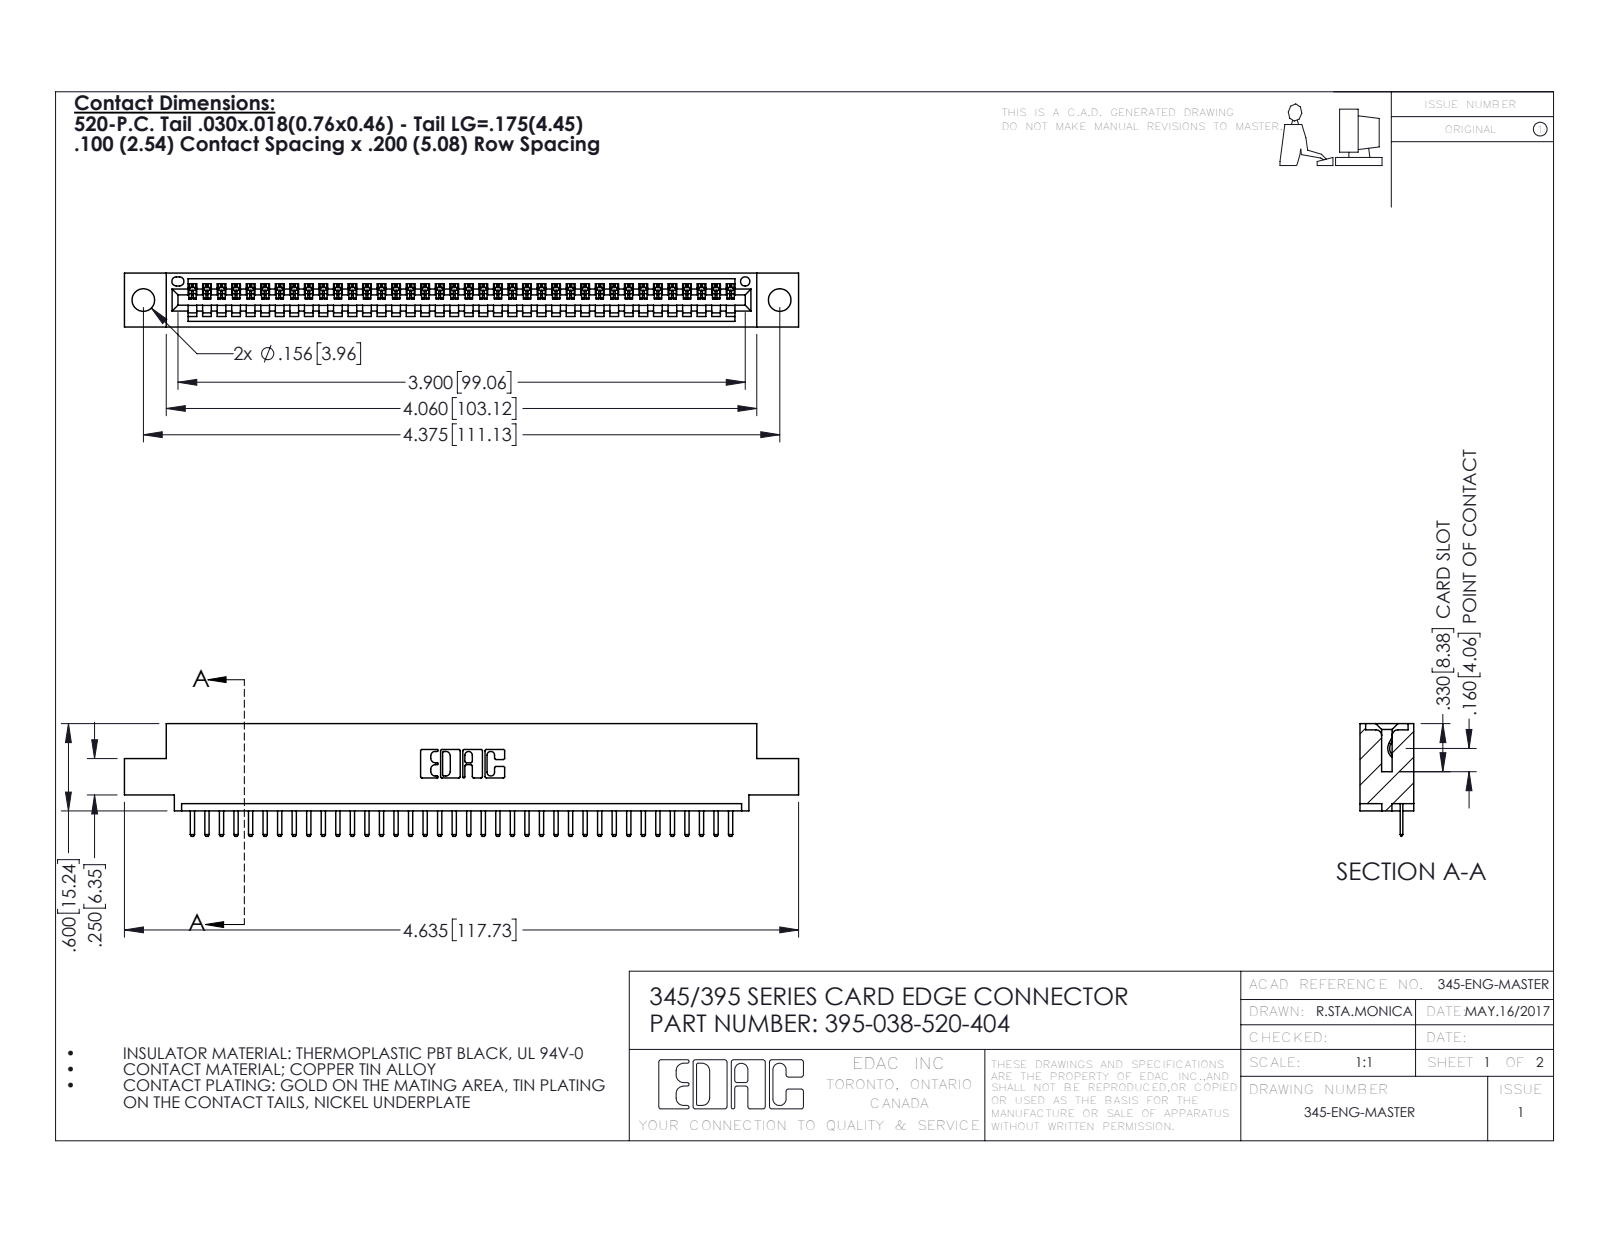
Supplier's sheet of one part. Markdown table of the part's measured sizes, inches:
| quantity | value |
| --- | --- |
| part name | 345 Part_0.110 Offset - 0.156 Dia-TH; 395-038-520-404; 345-292-001_345-293-120 |
| STEP written by | SolidWorks 2016 (CONFIG_CONTROL_DESIGN) |
| units | inches |
| bodies | 39 solids, 2486 faces (1680 planar, 806 cylindrical, 0 other) |
| overall size | 4.635 × 0.775 × 0.37 |
| volume | 0.664 in³ |
| surface area | 21.6 in² |
| round holes (diameter × count) | 0.156 × 2, 0.064 × 1 |
| partial cylindrical surfaces (radius × count) | 0.01 × 78, 0.006 × 76, 0.01 × 22, 0.007 × 6, 0.031 × 6, 0.026 × 3, 0.031 × 2, 0.04 × 2 |
| main face-to-face distances | 0.298, 0.072, 0.37, 0.2, 0.098, 0.272, 0.025, 0.225, 0.072, 0.149 |
| hole center spacings | 0.27, 4.139, 4.375 |
